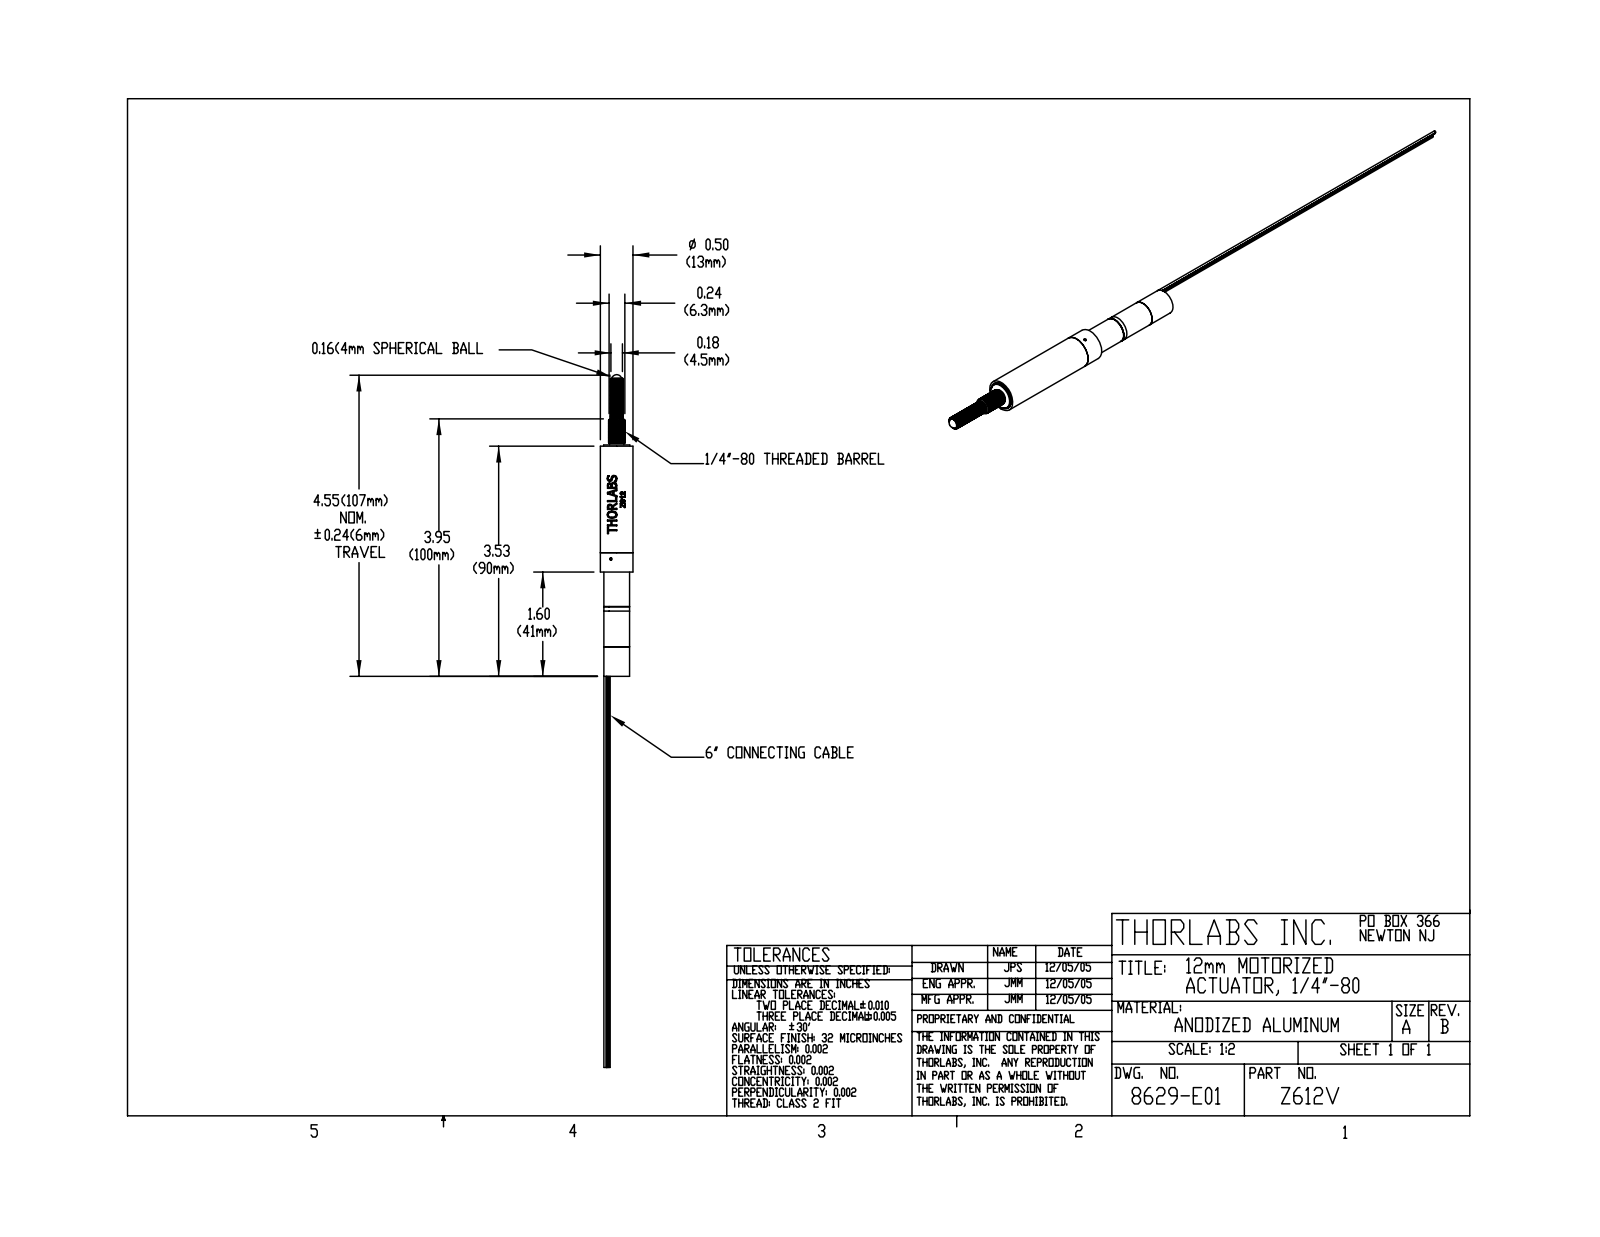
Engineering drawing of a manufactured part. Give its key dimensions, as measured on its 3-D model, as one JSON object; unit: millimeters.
{"part_name": "8629-E0W", "step_written_by": "SolidWorks 2007 (AUTOMOTIVE_DESIGN)", "units": "millimeters", "bodies": {"solids": 0, "faces": 247, "planar": 23, "cylindrical": 205, "other": 19}, "overall_size": [269.9, 12.7, 12.7], "round_holes": [[1, 1], [4, 1], [9.5, 1], [11, 1], [11.7, 1], [12.2, 1]], "round_bosses_or_shafts": [[12.7, 1], [10.2, 1], [10, 1], [10, 1], [6.4, 1], [5.6, 1], [5, 1]], "partial_cylinders_radius": [[0.4, 6]], "face_to_face_distances": [11.5, 78.7, 90.2, 63, 15.7, 27.2, 48, 15, 30.7, 42.2]}
